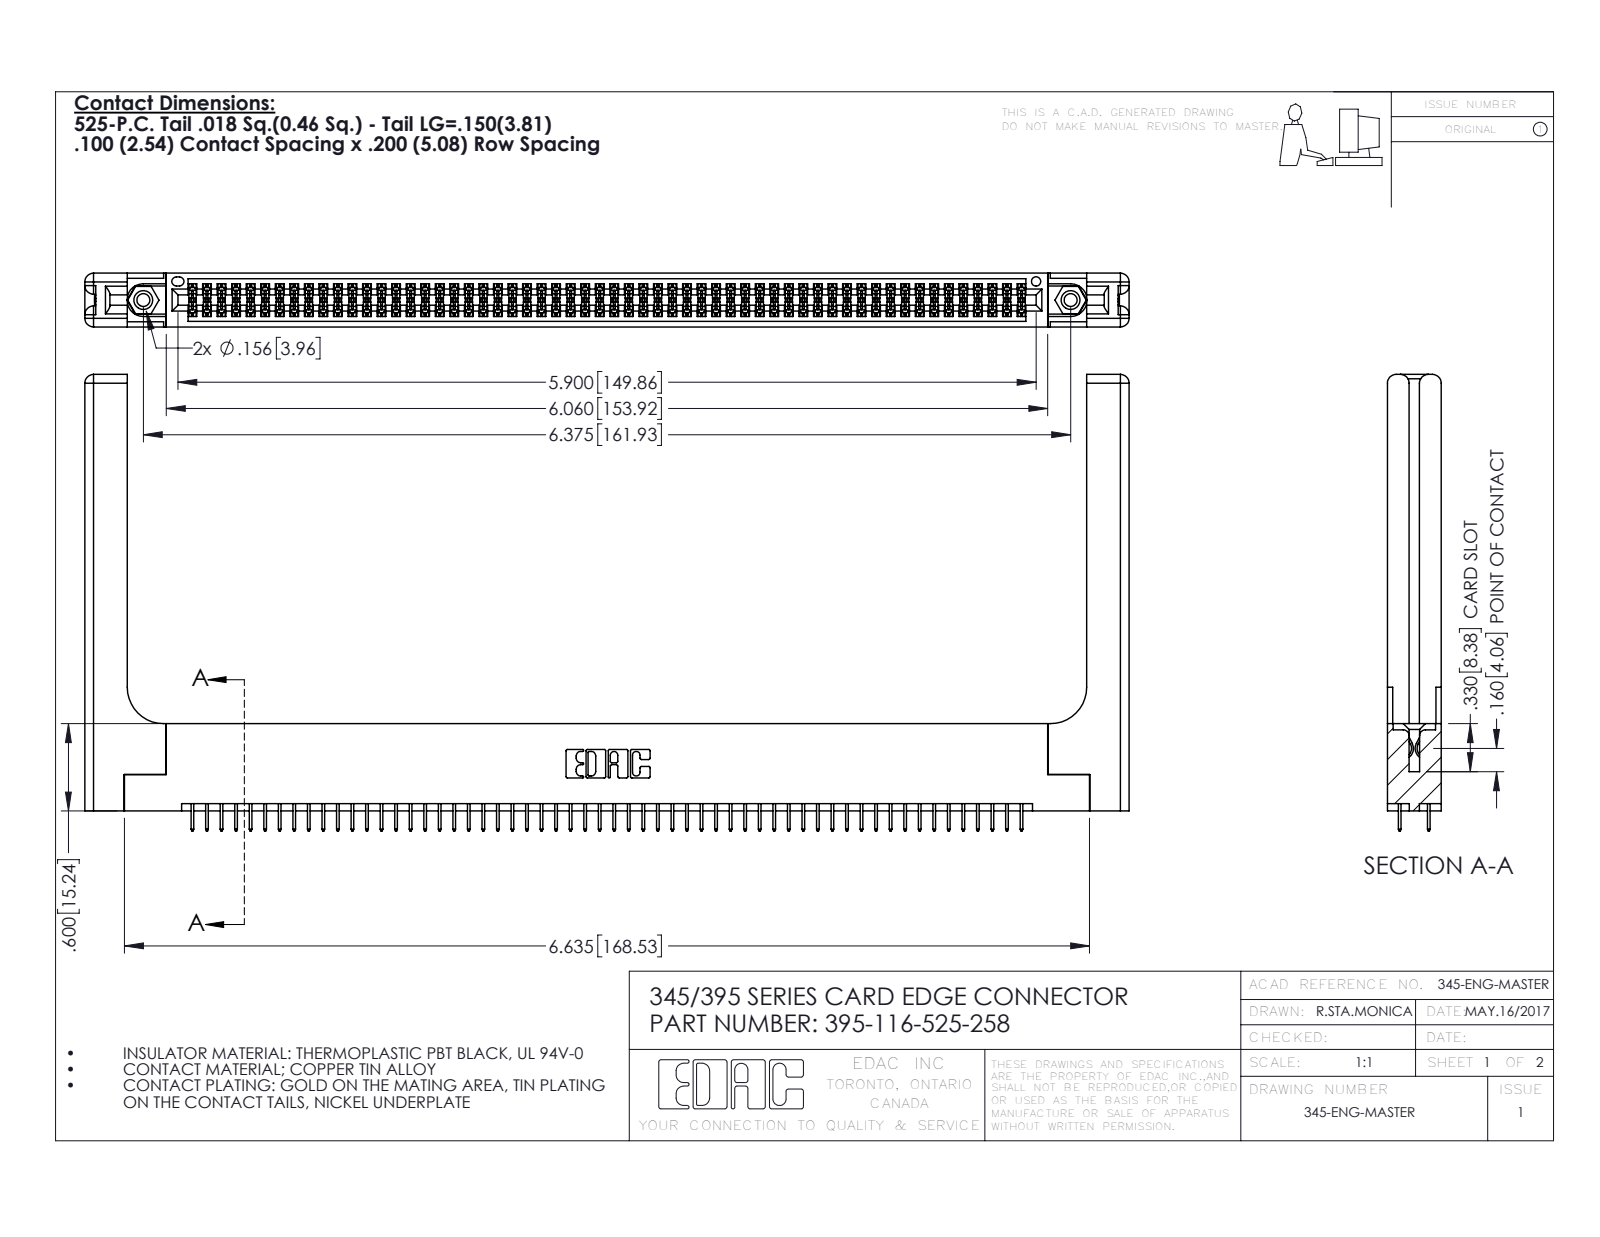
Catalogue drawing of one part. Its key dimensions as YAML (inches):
part_name: "345-250-001_345-250-001-102; 345 Part_Flush Mounting Lugs - 0.156 Dia-TH; 395-116-525-258; 345-292-001_345-293-125 (+1 more)"
step_written_by: "SolidWorks 2020 (CONFIG_CONTROL_DESIGN)"
units: inches
bodies: {solids: 121, faces: 6646, planar: 4752, cylindrical: 1834, other: 60}
overall_size: [7.179, 3.137, 0.37]
volume: 1.596
surface_area: 47.92
round_holes:
  - {diameter: 0.089, count: 2}
  - {diameter: 0.125, count: 2}
  - {diameter: 0.156, count: 2}
  - {diameter: 0.064, count: 1}
round_bosses_or_shafts:
  - {diameter: 0.155, count: 2}
partial_cylinders:
  - {radius: 0.006, count: 174}
  - {radius: 0.01, count: 22}
  - {radius: 0.06, count: 16}
  - {radius: 0.007, count: 6}
  - {radius: 0.031, count: 6}
  - {radius: 0.026, count: 3}
  - {radius: 0.014, count: 2}
  - {radius: 0.019, count: 2}
face_to_face_distances: [0.072, 0.298, 0.37, 0.2, 0.098, 0.272, 0.025, 0.225, 0.15, 0.148]
hole_center_spacings: [0.27, 6.139, 6.375]
